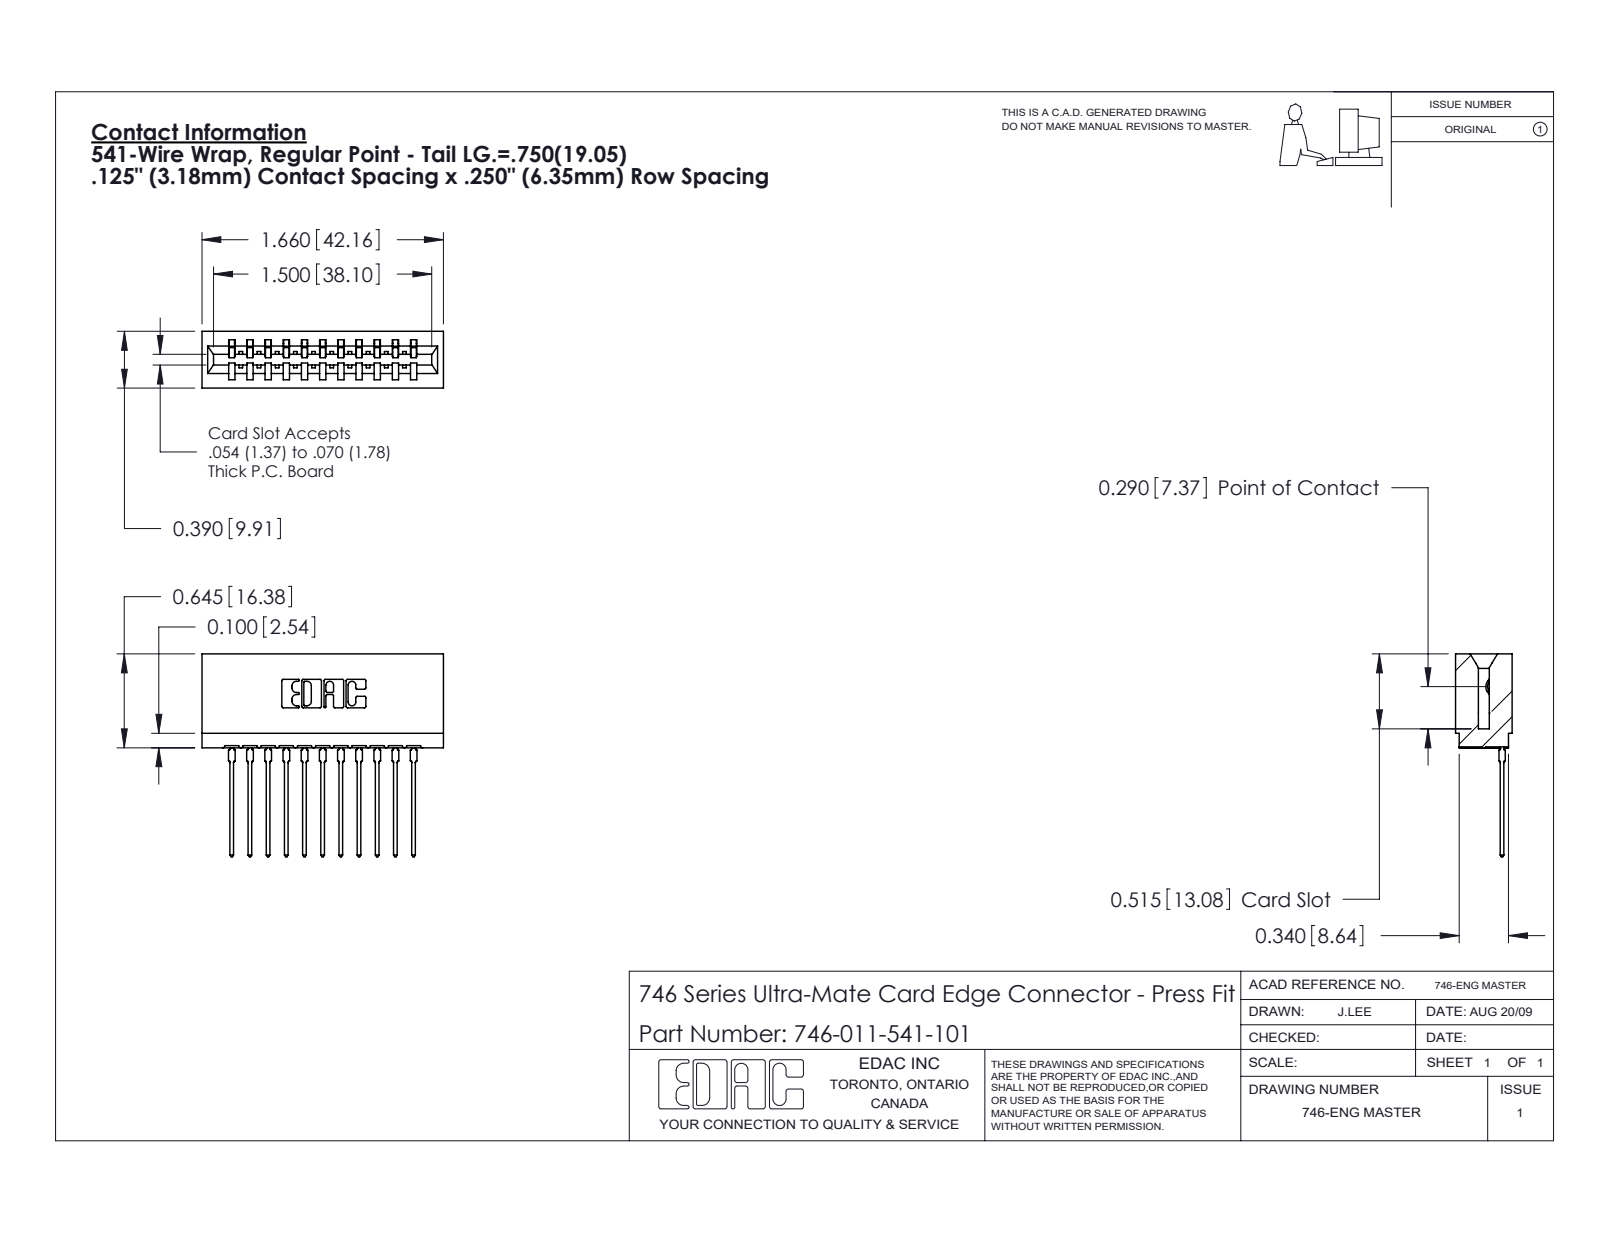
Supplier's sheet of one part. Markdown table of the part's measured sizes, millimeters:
| quantity | value |
| --- | --- |
| part name | 746 Part_.515 Slot Depth - 01; 746-011-541-101; 746-292-001_541 |
| STEP written by | SolidWorks 2020 (CONFIG_CONTROL_DESIGN) |
| units | millimeters |
| bodies | 12 solids, 1285 faces (748 planar, 251 cylindrical, 286 other) |
| overall size | 42.2 × 35.4 × 9.9 |
| volume | 4 670 mm³ |
| surface area | 6 665 mm² |
| partial cylindrical surfaces (radius × count) | 0.3 × 22, 0.5 × 22, 0.4 × 12, 0.2 × 6, 0.8 × 6, 0.1 × 4, 0.3 × 4, 0.7 × 3 |
| main face-to-face distances | 6.4, 8.5, 12.7, 1.4, 3.2, 3.2, 9.9, 1.1, 5.3, 2.1 |
